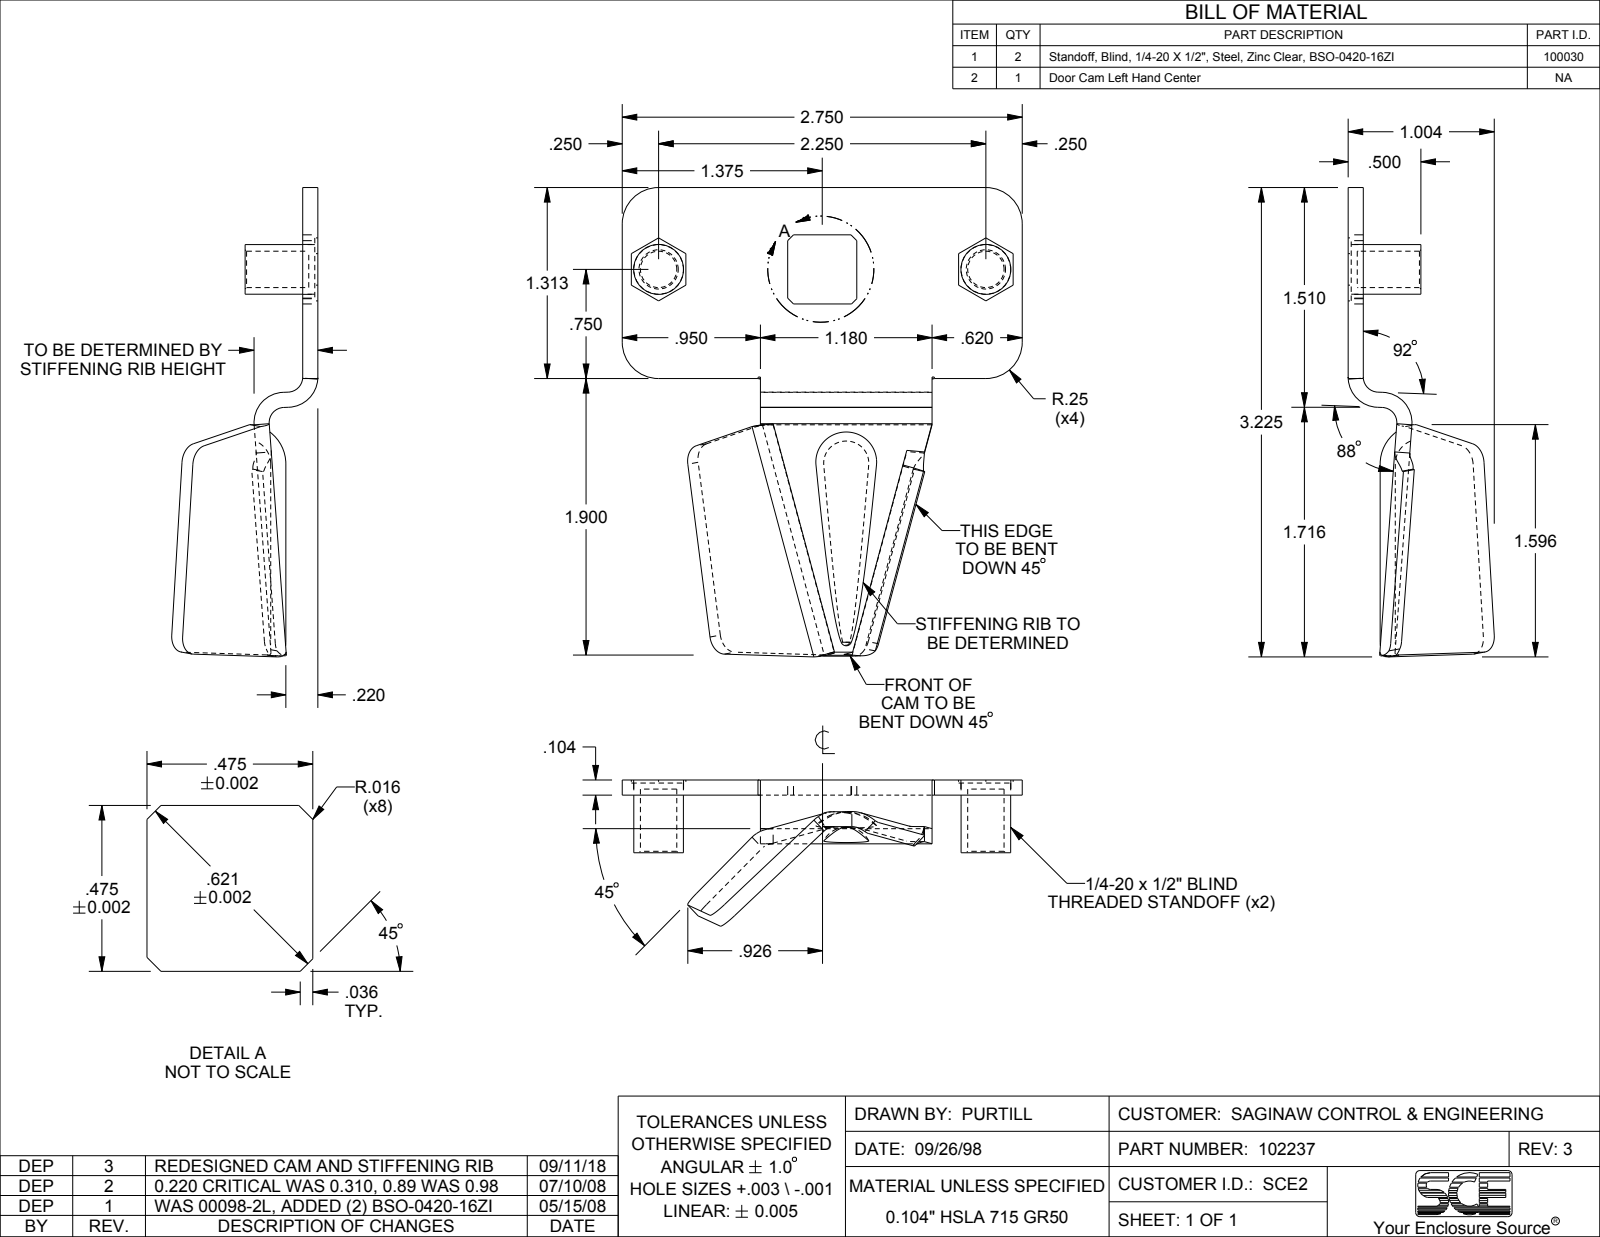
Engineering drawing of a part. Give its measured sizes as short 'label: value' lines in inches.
name: SCE-102237
written by: SolidWorks 2019 (AUTOMOTIVE_DESIGN)
unit: in
bodies: 3 solids, 97 faces (53 planar, 22 cylindrical, 22 other)
size: 3.215 × 2.75 × 1.005
volume: 0.703 in³; area: 16.54 in²
holes: 2× ⌀0.25, 2× ⌀0.343
bosses: 2× ⌀0.341
rounds: 4× R0.25, 3× R0.104, 3× R0.125, 3× R0.208, 1× R0.08, 1× R0.1, 1× R0.204
face distances: 0.104, 0.104, 1.313, 0.063, 0.041, 2.75, 1.137, 1.612, 0.475, 0.437
hole spacings: 2.25
